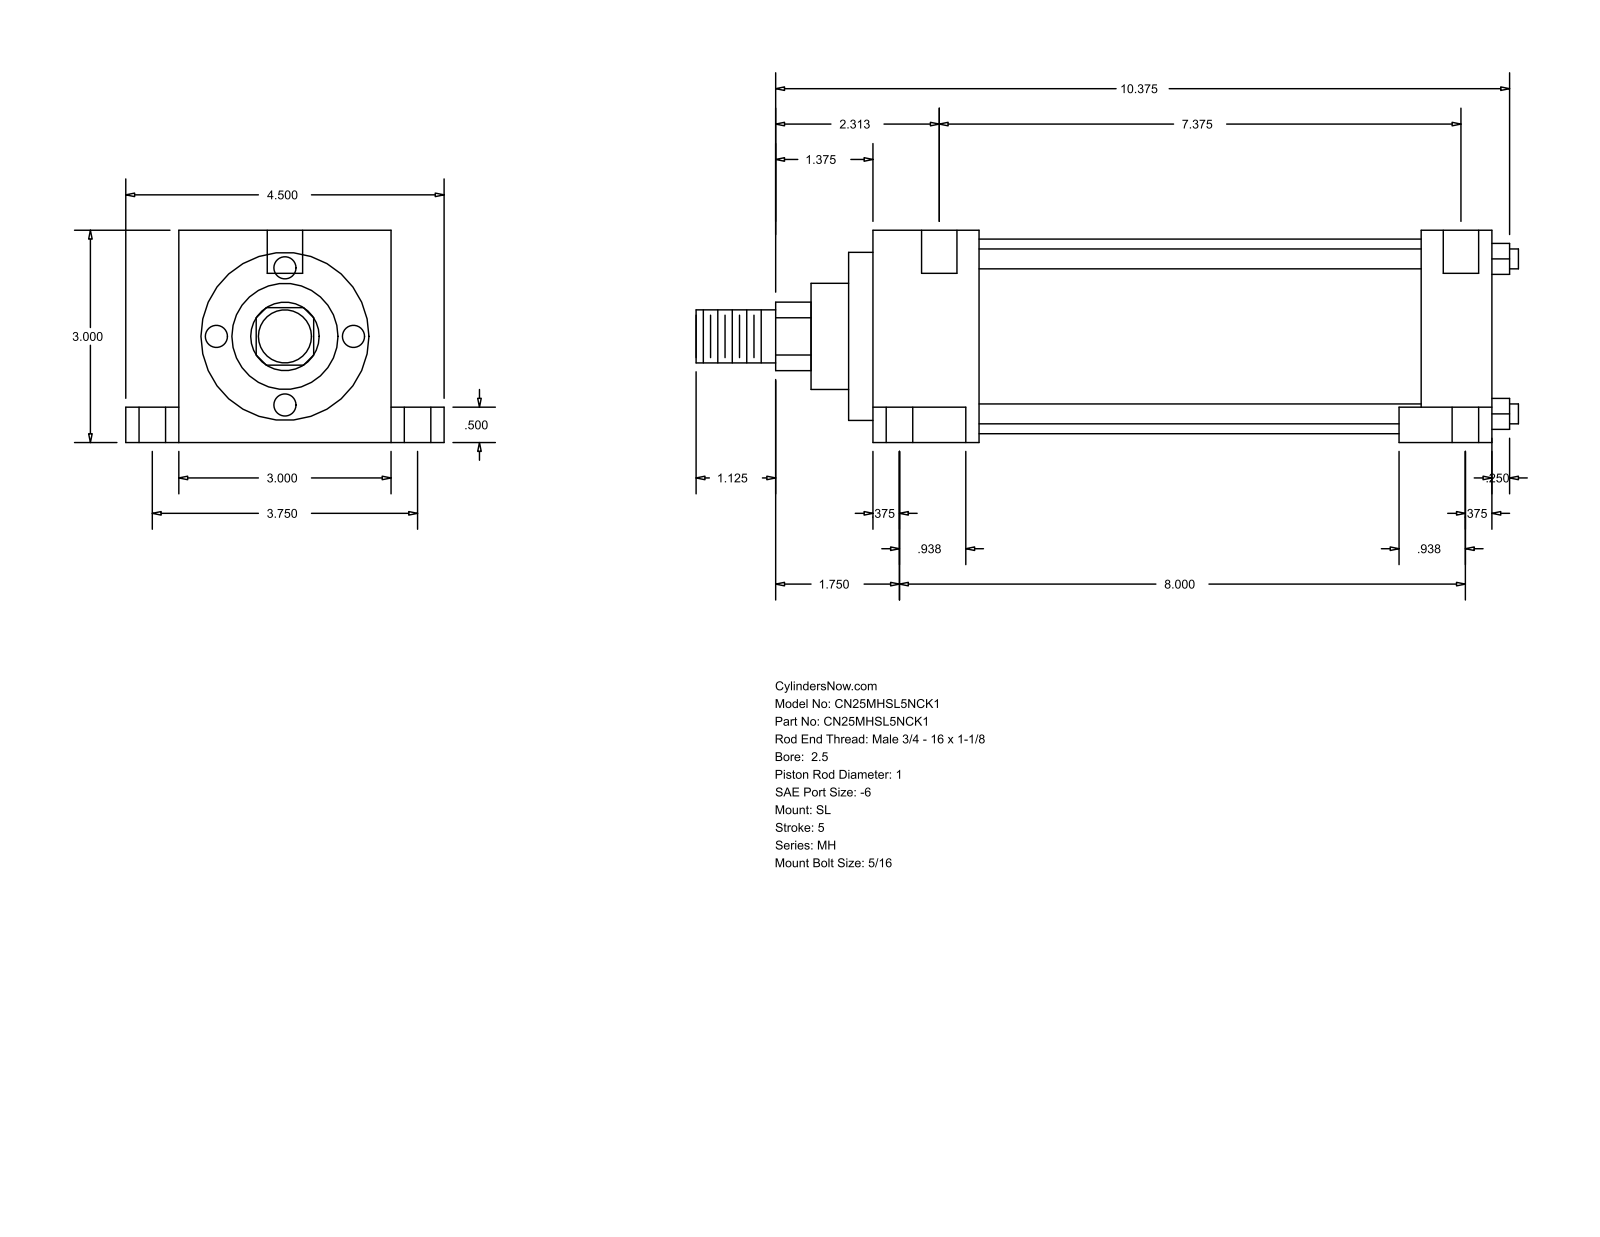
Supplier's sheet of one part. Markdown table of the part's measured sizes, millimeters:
| quantity | value |
| --- | --- |
| part name | MH_SL__0250_1 |
| STEP written by | GSSL Pune (CONFIG_CONTROL_DESIGN) |
| units | millimeters |
| bodies | 0 solids, 86 faces (61 planar, 25 cylindrical, 0 other) |
| overall size | 295.27 × 114.3 × 76.2 |
| round holes (diameter × count) | 5.56 × 2, 9.53 × 2, 15.88 × 2, 12.7 × 1 |
| round bosses / shafts (diameter × count) | 7.14 × 4, 69.85 × 1, 60.33 × 1, 38.1 × 1, 25.4 × 1, 19.05 × 1 |
| partial cylindrical surfaces (radius × count) | 12.29 × 1 |
| main face-to-face distances | 76.2, 25.4, 205.59, 230.99, 12.7, 63.5, 19.05, 95.25, 13.49, 219.08 |
| hole center spacings | 47.65, 3.18, 95.24 |
